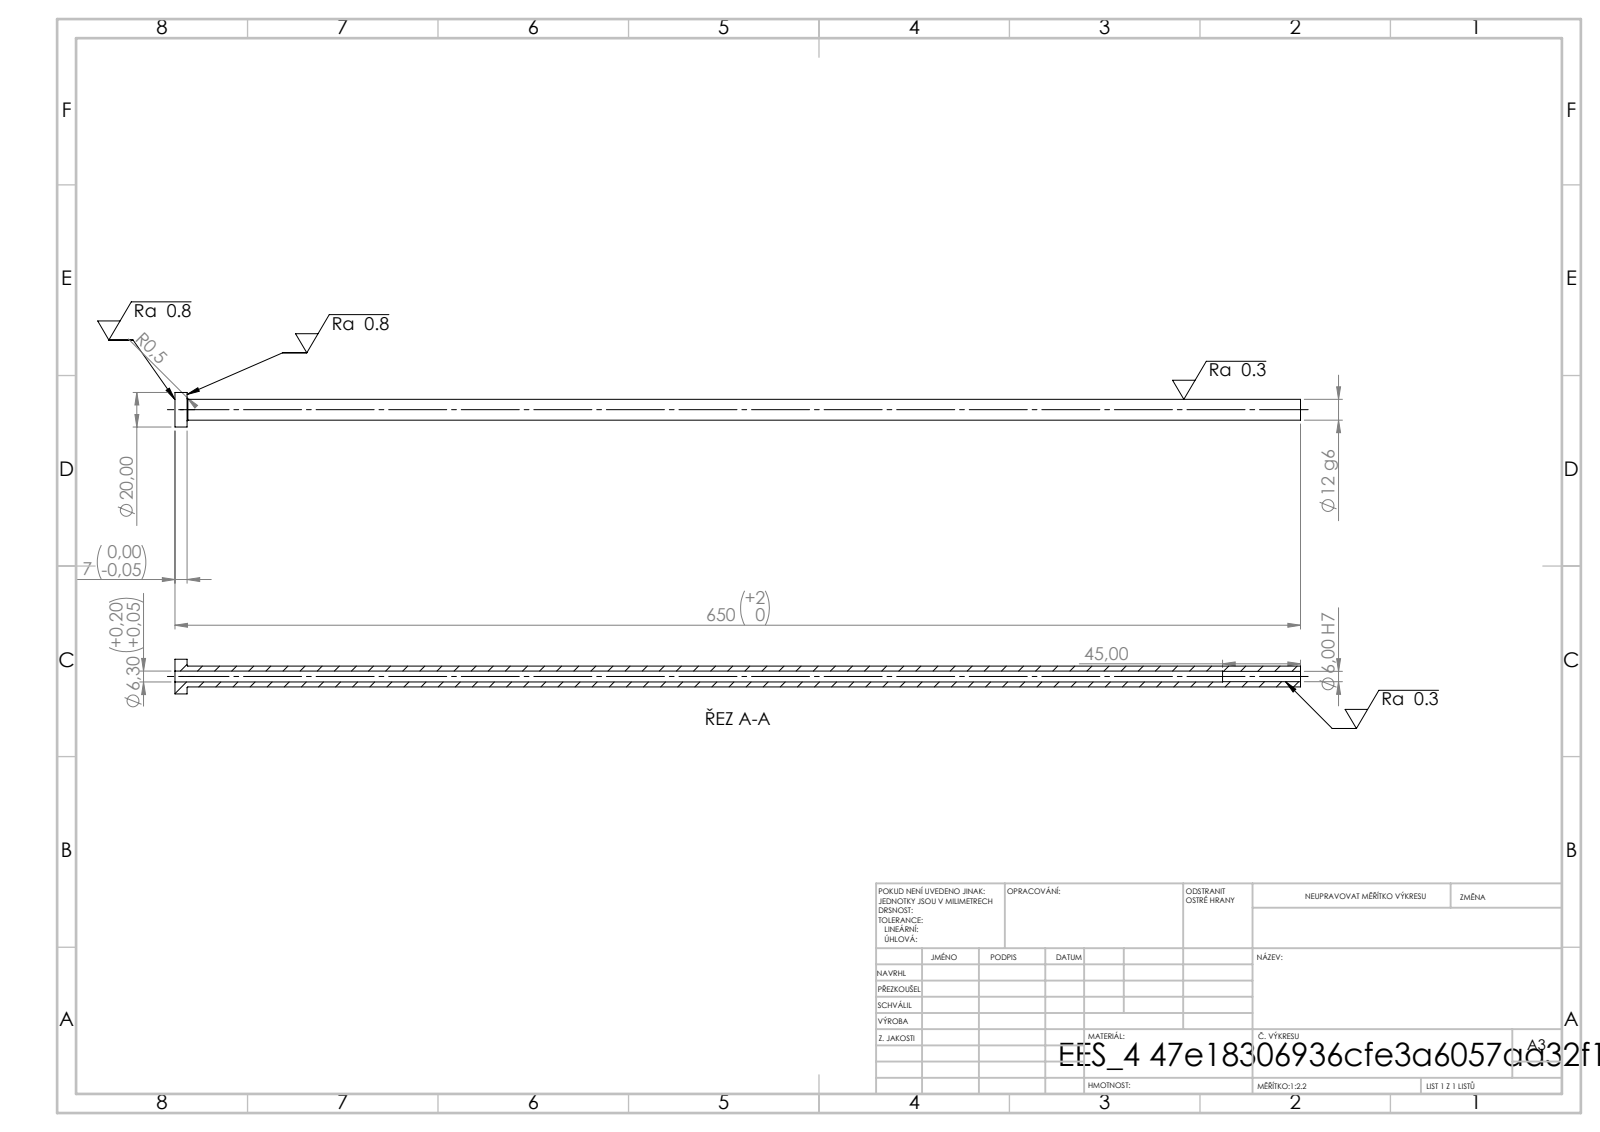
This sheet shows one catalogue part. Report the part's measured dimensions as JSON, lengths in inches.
{"step_written_by": "SolidWorks 2019 (CONFIG_CONTROL_DESIGN)", "units": "inches", "bodies": {"solids": 1, "faces": 14, "planar": 4, "cylindrical": 8, "other": 2}, "overall_size": [25.591, 0.787, 0.787], "volume_in3": 3.344, "surface_area_in2": 59, "round_holes": [[0.236, 1], [0.248, 1]], "round_bosses_or_shafts": [[0.787, 1], [0.472, 1]], "face_to_face_distances": [0.276, 25.591, 25.315, 23.819, 23.543, 1.772]}
